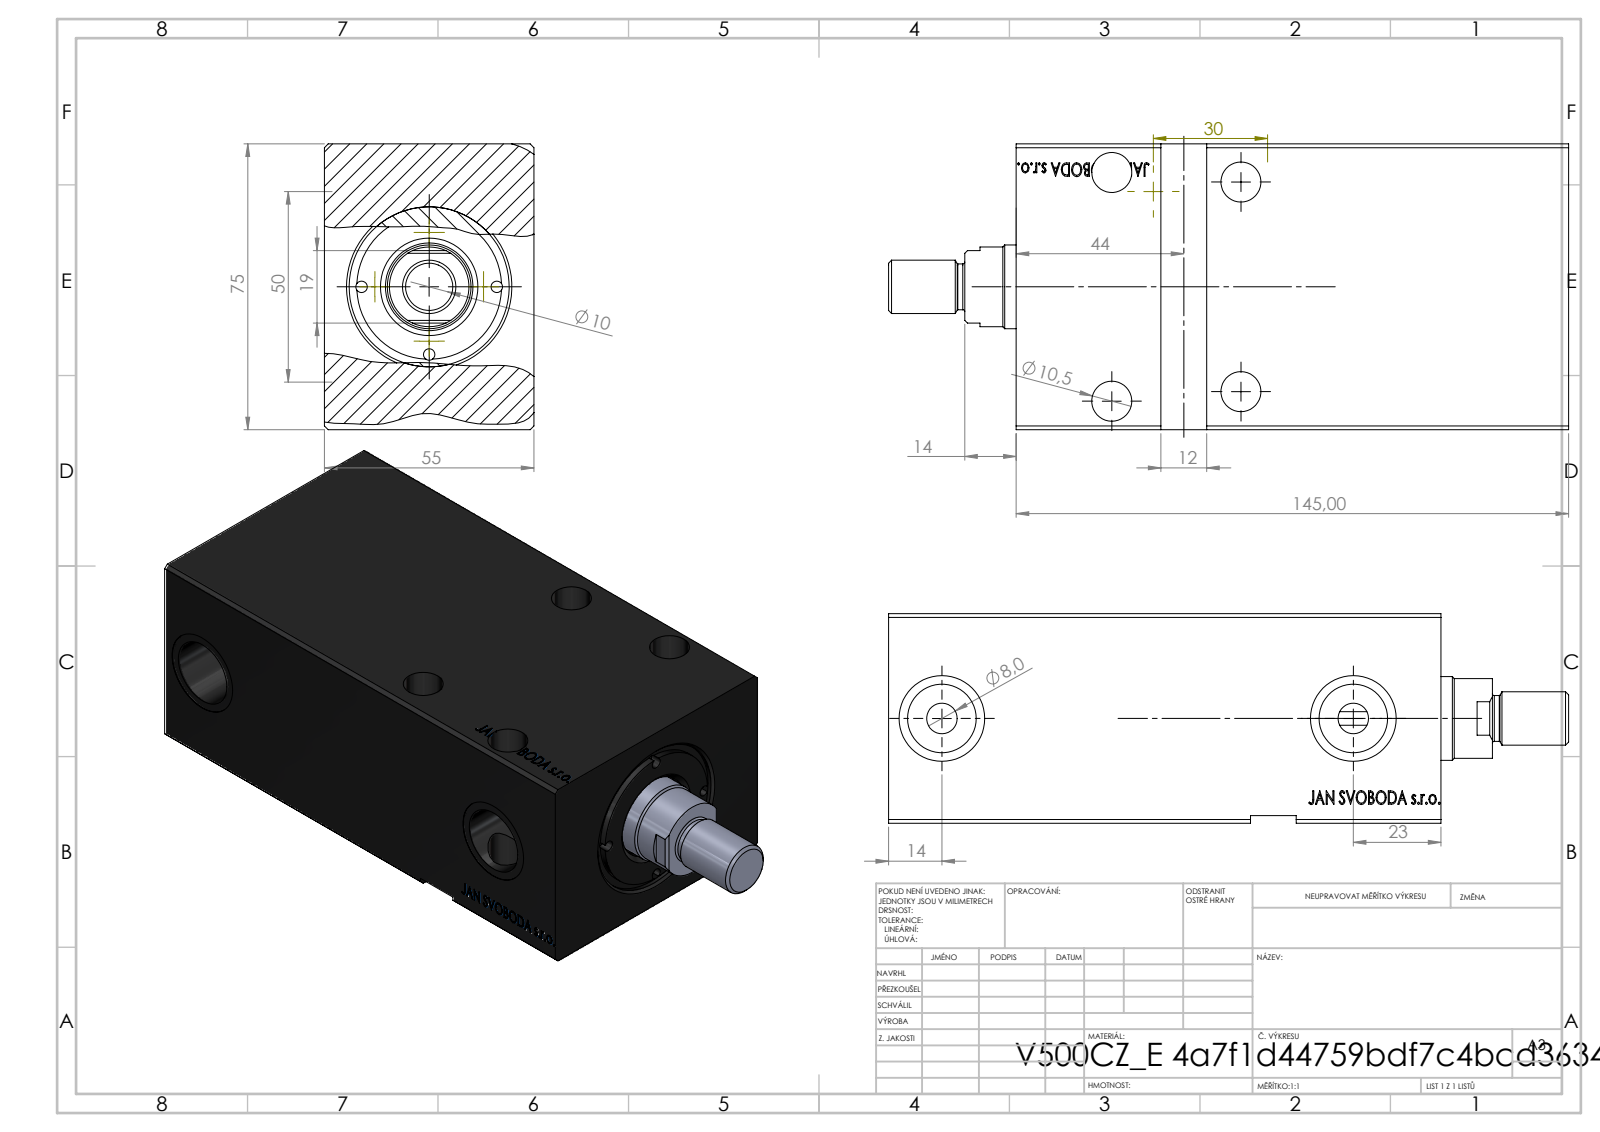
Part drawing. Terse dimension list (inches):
name: V500CZ_E; V500CZ_VCP_E; V500CZ_FM; V500CZ_VC_vysunovaci_E
written by: SolidWorks 2019 (CONFIG_CONTROL_DESIGN)
unit: in
bodies: 4 solids, 796 faces (378 planar, 58 cylindrical, 360 other)
size: 7.028 × 2.953 × 2.165
volume: 33.17 in³; area: 128.7 in²
holes: 4× ⌀0.118, 4× ⌀0.413, 2× ⌀0.315, 2× ⌀0.709, 2× ⌀0.886, 1× ⌀0.394, 1× ⌀0.866, 1× ⌀0.906, 1× ⌀1.26, 1× ⌀1.417, 1× ⌀1.654
bosses: 1× ⌀1.496, 1× ⌀0.824, 1× ⌀0.551, 1× ⌀0.472
face distances: 2.165, 2.953, 5.709, 4.528, 1.181, 5.701, 1.173, 0.465, 4.063, 5.236
hole spacings: 0.699, 0.988, 1.339, 1.398, 2.628, 2.165, 2.362, 4.252
